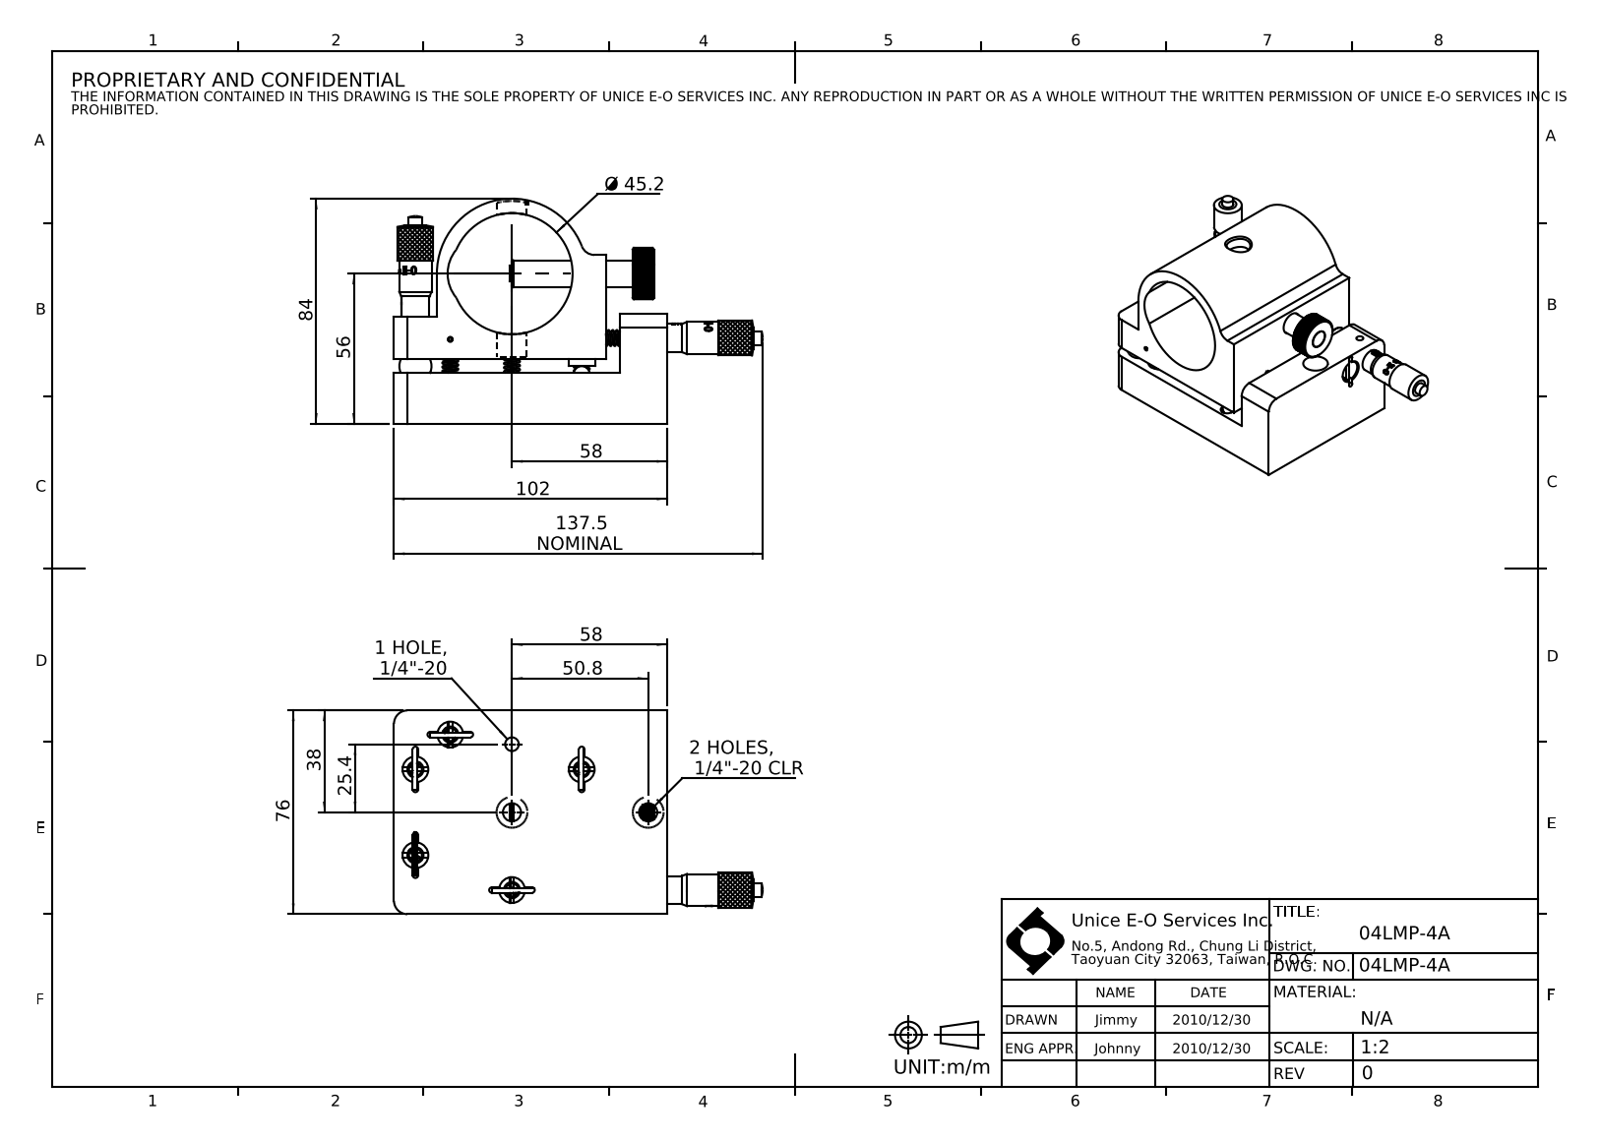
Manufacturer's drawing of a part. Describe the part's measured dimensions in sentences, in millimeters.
The part is named "04LMP-4A". Its 3-D file was written by "SolidWorks 2016 (CONFIG_CONTROL_DESIGN)". It is 31 solids with 1390 faces: 589 planar, 412 cylindrical and 389 other. Overall it measures 137.5 by 84 by 76 millimeters. Its volume is 315 776 cubic millimeters and its surface area 86 455 square millimeters. Round holes: 10 of diameter 1.2, 6 of diameter 9.6, 5 of diameter 1.8, 2 of diameter 2.5, 2 of diameter 3.3, 2 of diameter 5, 2 of diameter 6.76, 2 of diameter 9.5, 2 of diameter 10.6, 2 of diameter 11.51, 2 of diameter 12.7, 1 of diameter 5.11. Round bosses or shafts: 10 of diameter 1.6, 7 of diameter 0.6, 3 of diameter 6, 2 of diameter 13, 2 of diameter 12, 2 of diameter 10.5, 2 of diameter 9.9, 2 of diameter 9.2. Partial cylindrical surfaces (rounded edges, fillets, slot ends): 72 of radius 0.1, 12 of radius 1, 5 of radius 5, 4 of radius 3, 2 of radius 5.98, 1 of radius 9.5, 1 of radius 14, 1 of radius 28. The main face-to-face distances are 5, 19, 24, 76, 23, 16, 102, 79, 63, 17.9. The hole center spacings are 13, 4, 13.6, 25.61, 29, 32, 32.14, 33.8.
